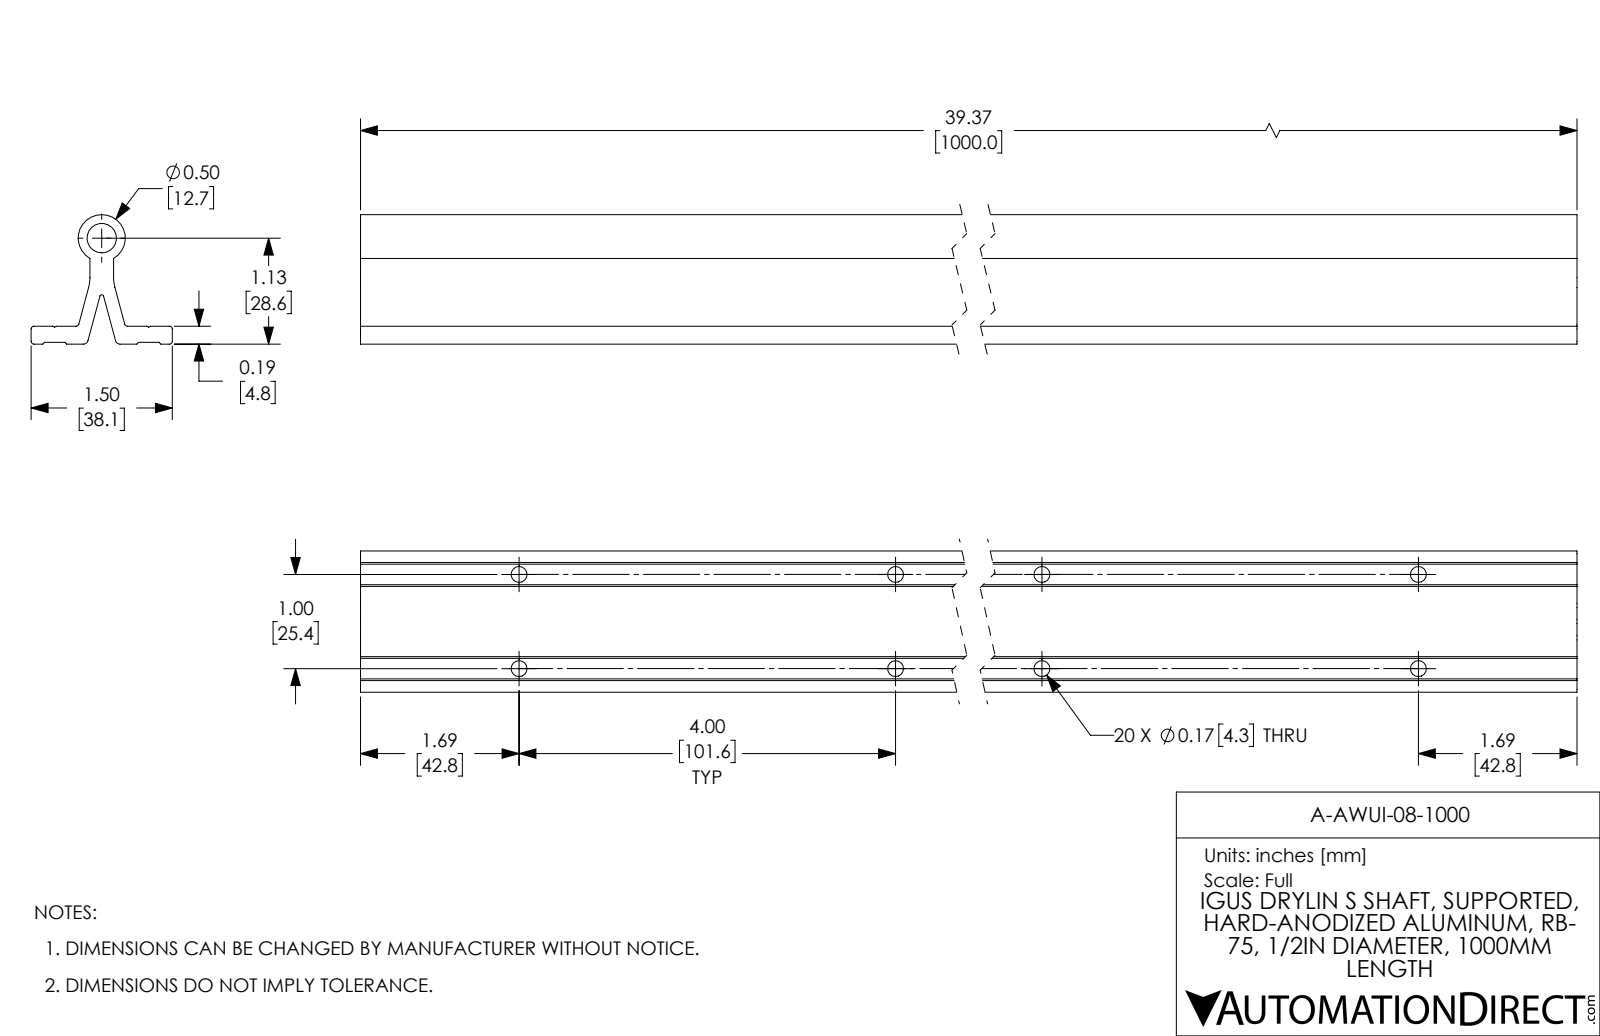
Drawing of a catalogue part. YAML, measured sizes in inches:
part_name: "A-AWUI-08-1000"
step_written_by: "SolidWorks 2017 (AUTOMOTIVE_DESIGN)"
units: inches
bodies: {solids: 1, faces: 122, planar: 68, cylindrical: 54, other: 0}
overall_size: [39.37, 1.5, 1.375]
volume: 21.07
surface_area: 292.9
round_holes:
  - {diameter: 0.169, count: 20}
  - {diameter: 0.313, count: 1}
round_bosses_or_shafts:
  - {diameter: 0.5, count: 1}
partial_cylinders:
  - {radius: 0.03, count: 6}
  - {radius: 0.05, count: 2}
  - {radius: 0.394, count: 2}
  - {radius: 0.02, count: 1}
face_to_face_distances: [0.14, 0.19, 0.019, 0.171, 0.624, 0.876, 0.252, 1.5, 0.707, 0.456]
hole_center_spacings: [4, 4.123, 8, 8.062, 12, 12.042, 16, 16.031]
